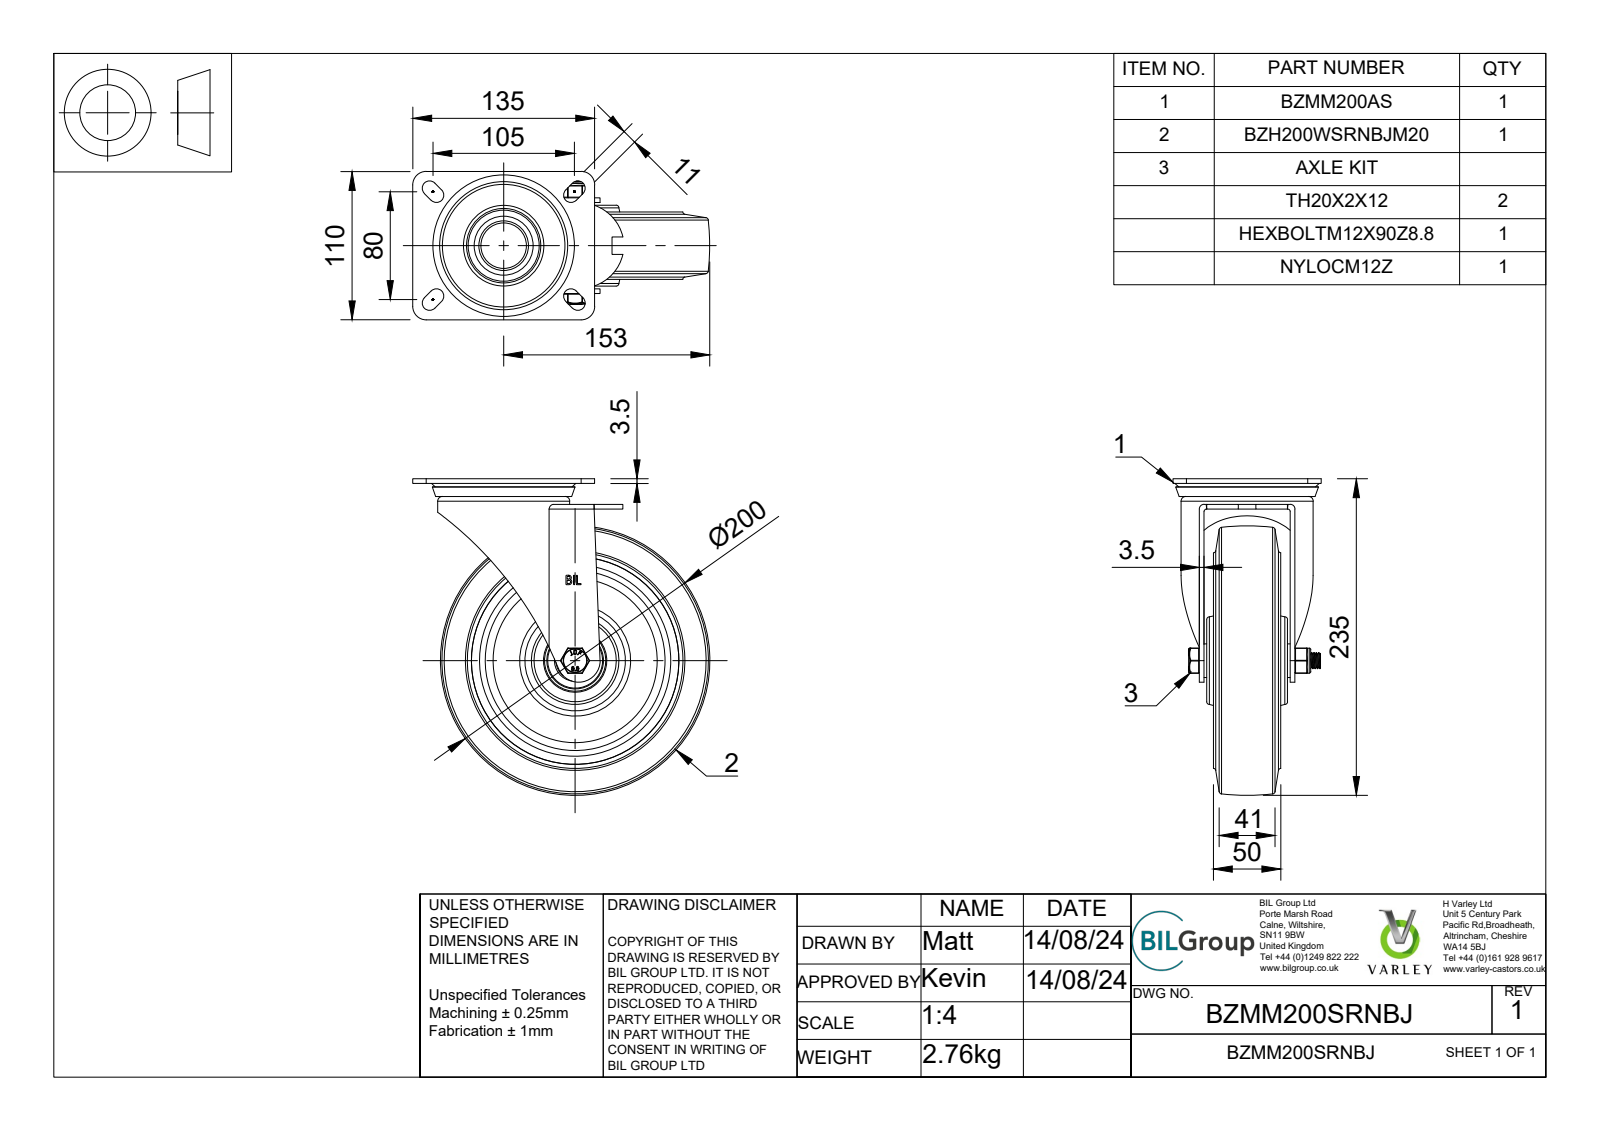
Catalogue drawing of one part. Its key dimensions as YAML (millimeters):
part_name: "BZMM200SRNBJ v3; BZMM200AS - 2 - 64 v1; ZINC PLATED, PRESSED STEEL TOP PLATE; ZINC PLATED, PRESSED STEEL TOP PLATE Geometry (+7 more)"
step_written_by: "Autodesk Translation Framework v13.14.0.145 (AUTOMOTIVE_DESIGN)"
units: millimeters
bodies: {solids: 77, faces: 1159, planar: 464, cylindrical: 206, other: 489}
overall_size: [235, 220.5, 110]
volume: 1231000
surface_area: 318211
round_holes:
  - {diameter: 12, count: 1}
  - {diameter: 12.2, count: 1}
  - {diameter: 14, count: 1}
  - {diameter: 20, count: 1}
  - {diameter: 28.5, count: 1}
  - {diameter: 30.8, count: 1}
  - {diameter: 33.75, count: 1}
  - {diameter: 40.3, count: 1}
  - {diameter: 40.5, count: 1}
  - {diameter: 42, count: 1}
  - {diameter: 44, count: 1}
  - {diameter: 47, count: 1}
round_bosses_or_shafts:
  - {diameter: 98, count: 1}
  - {diameter: 78, count: 1}
  - {diameter: 50, count: 1}
  - {diameter: 40.8, count: 1}
  - {diameter: 39.75, count: 1}
  - {diameter: 31.3, count: 1}
  - {diameter: 27, count: 1}
  - {diameter: 25, count: 1}
partial_cylinders:
  - {radius: 0.5, count: 19}
  - {radius: 5.5, count: 8}
  - {radius: 0.47, count: 4}
  - {radius: 0.9, count: 4}
  - {radius: 1.75, count: 4}
  - {radius: 10, count: 4}
  - {radius: 0.89, count: 2}
  - {radius: 0.89, count: 2}
face_to_face_distances: [3.5, 7, 27, 37, 10, 9, 40.5, 5.5, 30.5, 67.5]
